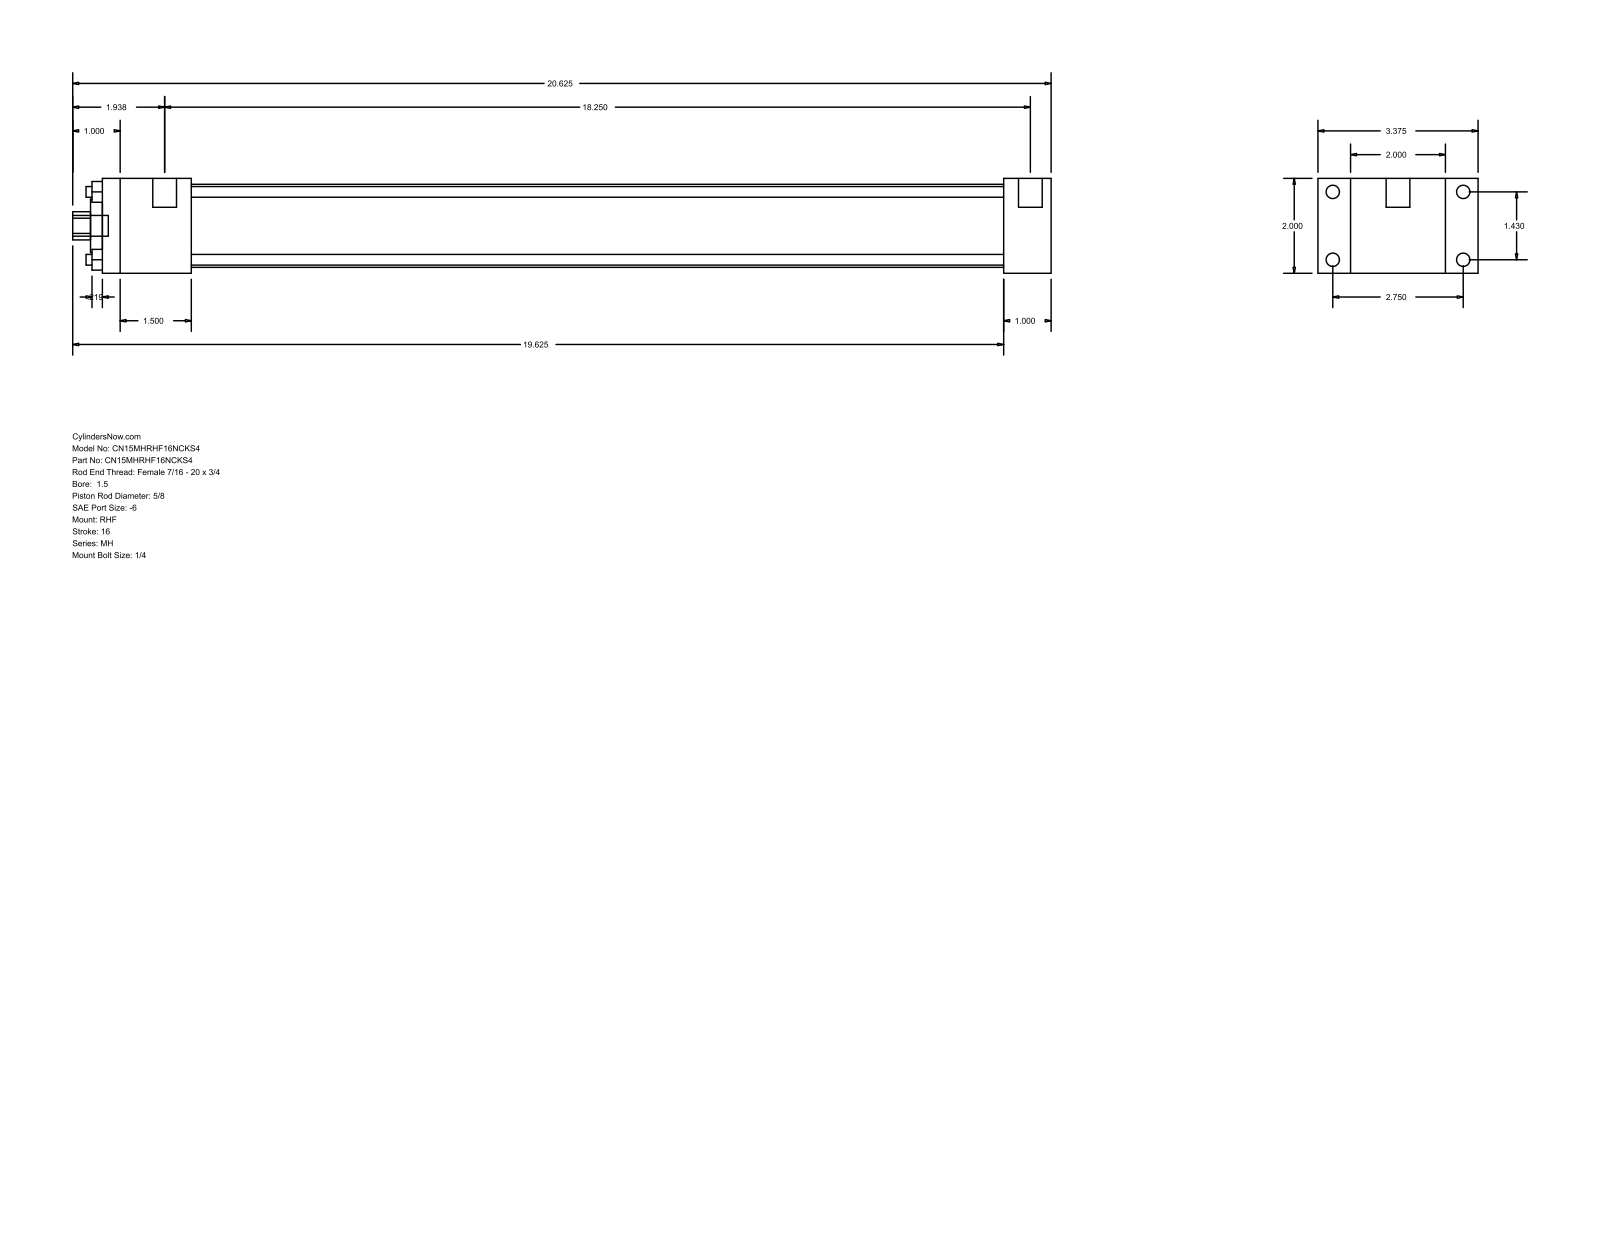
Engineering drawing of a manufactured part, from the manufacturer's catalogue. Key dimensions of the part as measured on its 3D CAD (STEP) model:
Part name (STEP PRODUCT): MH_RHF__0150_0.625
STEP written by: GSSL Pune (CONFIG_CONTROL_DESIGN)
Units: millimetres
Bodies: 0 solids, 88 faces (60 planar, 28 cylindrical, 0 other)
Overall size (bounding box): 523.88 × 85.72 × 50.8
Round holes (diameter × count): ⌀5.71 ×4, ⌀15.88 ×1, ⌀28.57 ×1, ⌀44.45 ×1
Round bosses / shafts (diameter × count): ⌀7.14 ×4, ⌀5.56 ×4, ⌀12.7 ×2, ⌀11.11 ×1
Partial cylindrical surfaces — rounded edges, fillets, slot ends (radius × count): R7.54 ×1
Main face-to-face distances: 50.8, 17.46, 68.26, 25.4, 482.6, 508, 85.72, 47.62, 434.98, 460.38
Hole centre spacings: 25.68, 36.32, 51.36
